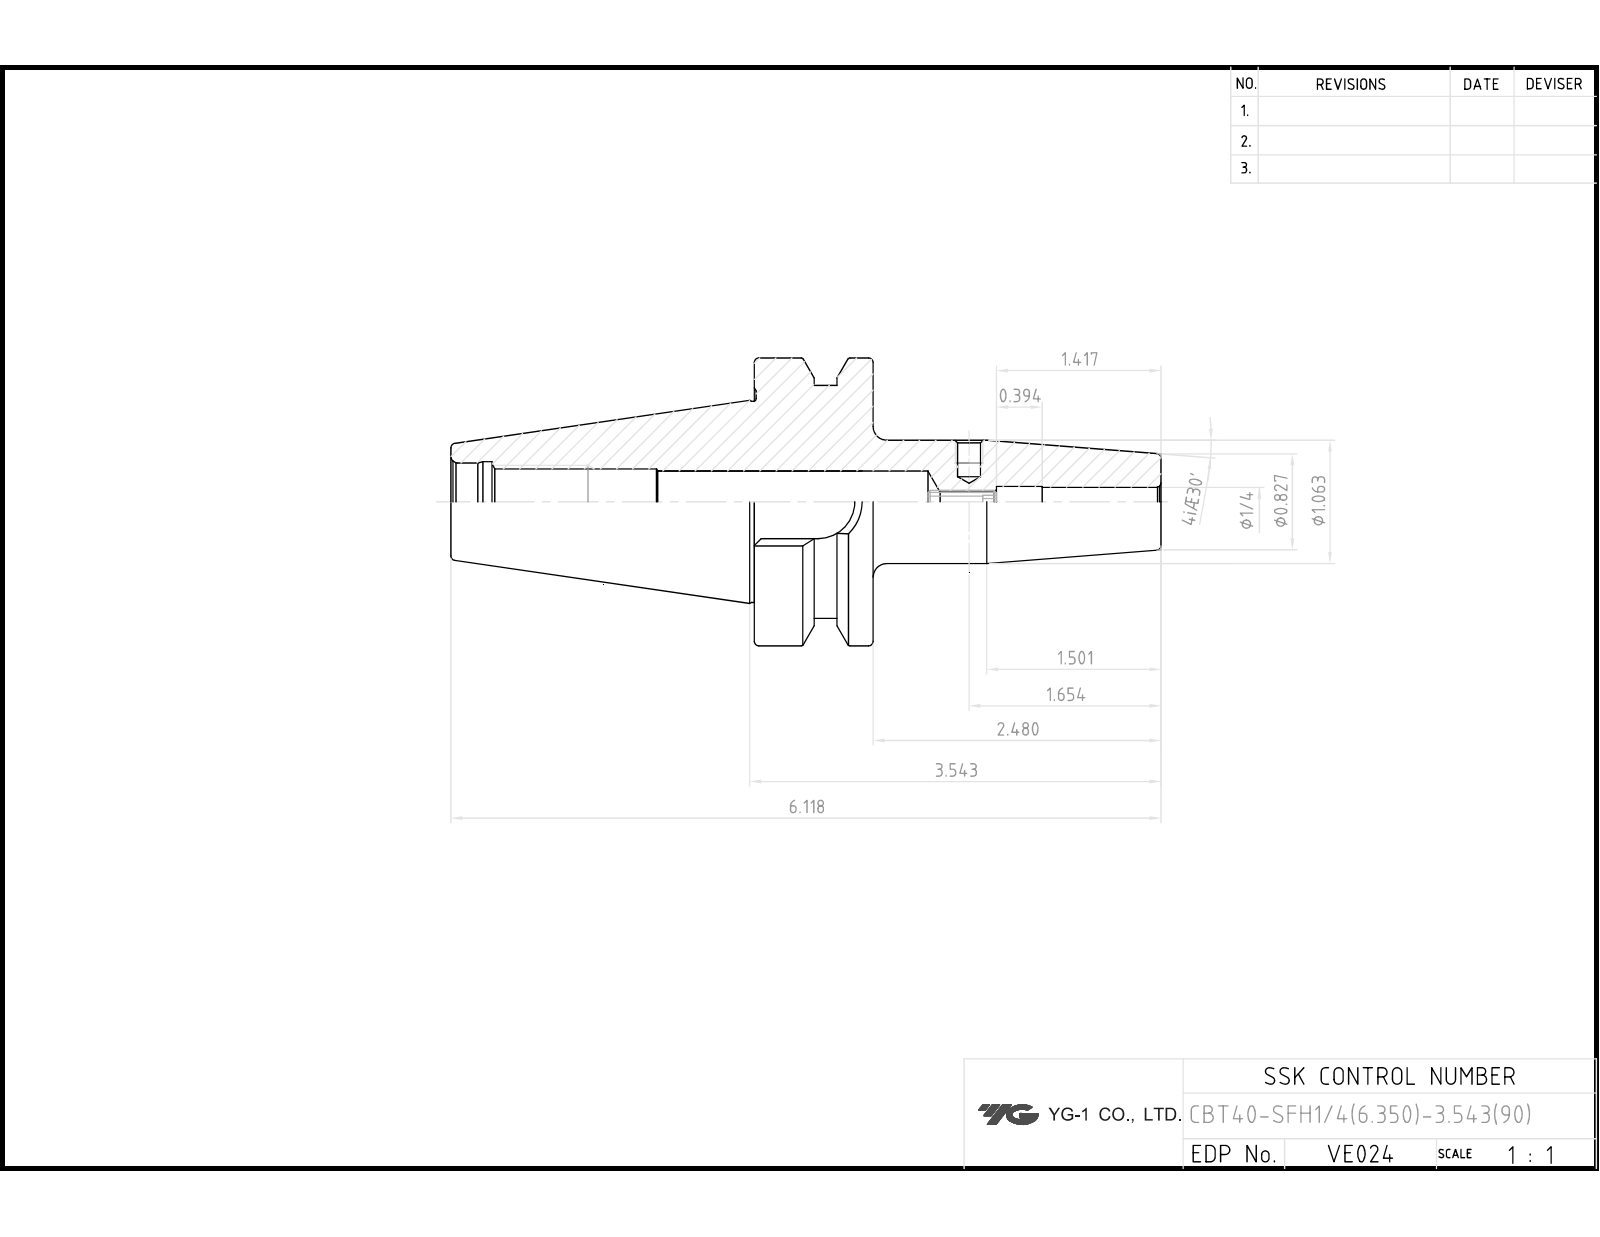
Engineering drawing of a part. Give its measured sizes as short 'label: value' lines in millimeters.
name: LO-CBT40-SFH6.35-90
written by: Autodesk Inventor 2025 (AUTOMOTIVE_DESIGN)
unit: mm
bodies: 1 solid, 61 faces (24 planar, 15 cylindrical, 22 other)
size: 155.4 × 63 × 63
volume: 150 758 mm³; area: 28 474 mm²
holes: 1× ⌀4.3, 1× ⌀6.35, 1× ⌀7.55, 1× ⌀13.84, 1× ⌀17, 1× ⌀17.6
bosses: 1× ⌀63, 1× ⌀52.6, 1× ⌀44, 1× ⌀27
rounds: 1× R8.05
face distances: 26, 45.2, 63, 89, 0.4, 25.6, 88.6, 16.1, 66.4, 66.8
